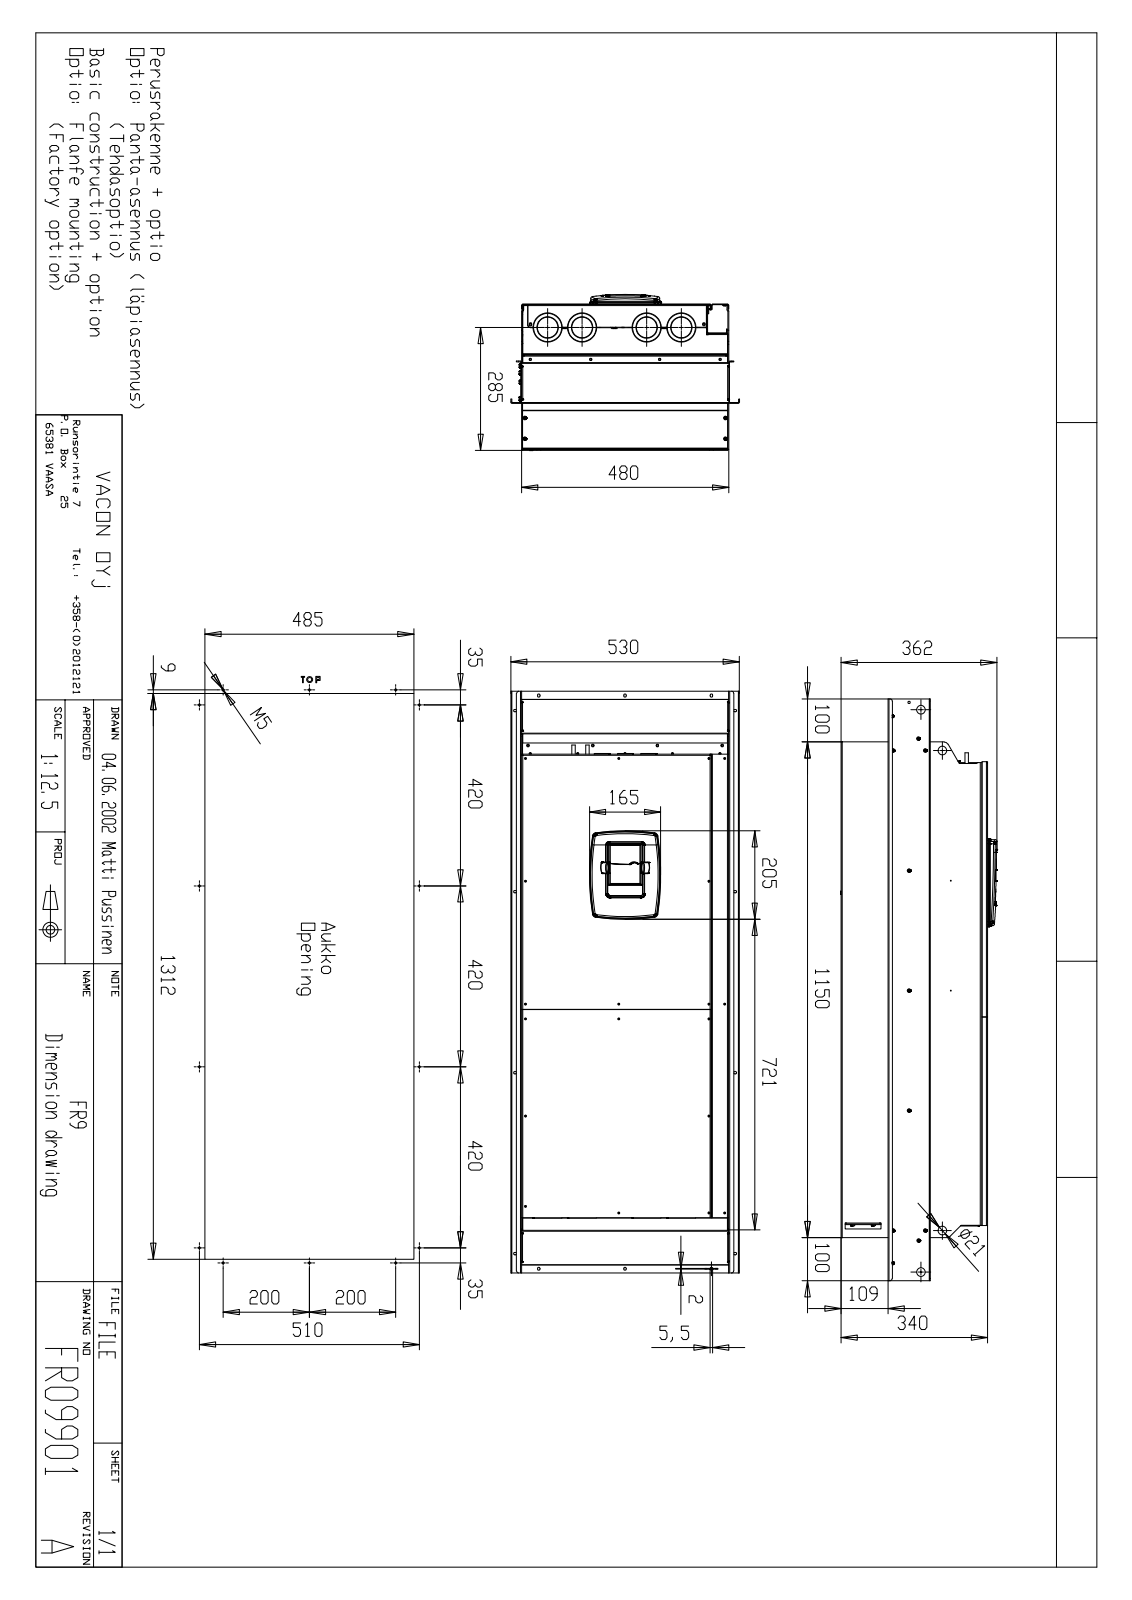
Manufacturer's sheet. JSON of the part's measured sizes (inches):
{"part_name": "FR09_COLLAR", "step_written_by": "CREO PARAMETRIC BY PTC INC, 2018070 (CONFIG_CONTROL_DESIGN)", "units": "inches", "bodies": {"solids": 10, "faces": 6709, "planar": 2743, "cylindrical": 3214, "other": 752}, "overall_size": [53.15, 20.866, 14.253], "volume_in3": 353.6, "surface_area_in2": 12550, "round_holes": [[0.142, 76], [0.181, 66], [0.177, 48], [0.13, 37], [0.217, 29], [0.118, 21], [0.098, 11], [0.169, 8], [0.205, 8], [0.236, 8], [3.063, 8], [0.63, 5]], "round_bosses_or_shafts": [[0.197, 31], [0.157, 30], [0.394, 28], [0.295, 17], [0.315, 15], [0.374, 11], [0.236, 9], [0.18, 9]], "partial_cylinders_radius": [[0.017, 222], [0.035, 222], [0.138, 171], [0.157, 94], [0.236, 75], [0.015, 74], [0.093, 67], [0.039, 59]], "face_to_face_distances": [0.079, 0.059, 18.819, 18.898, 13.228, 13.307, 13.366, 13.287, 18.74, 0.165], "hole_center_spacings": [1.736, 4.252, 3.543, 5.535, 18.307, 2.455, 2.621, 3.264]}
